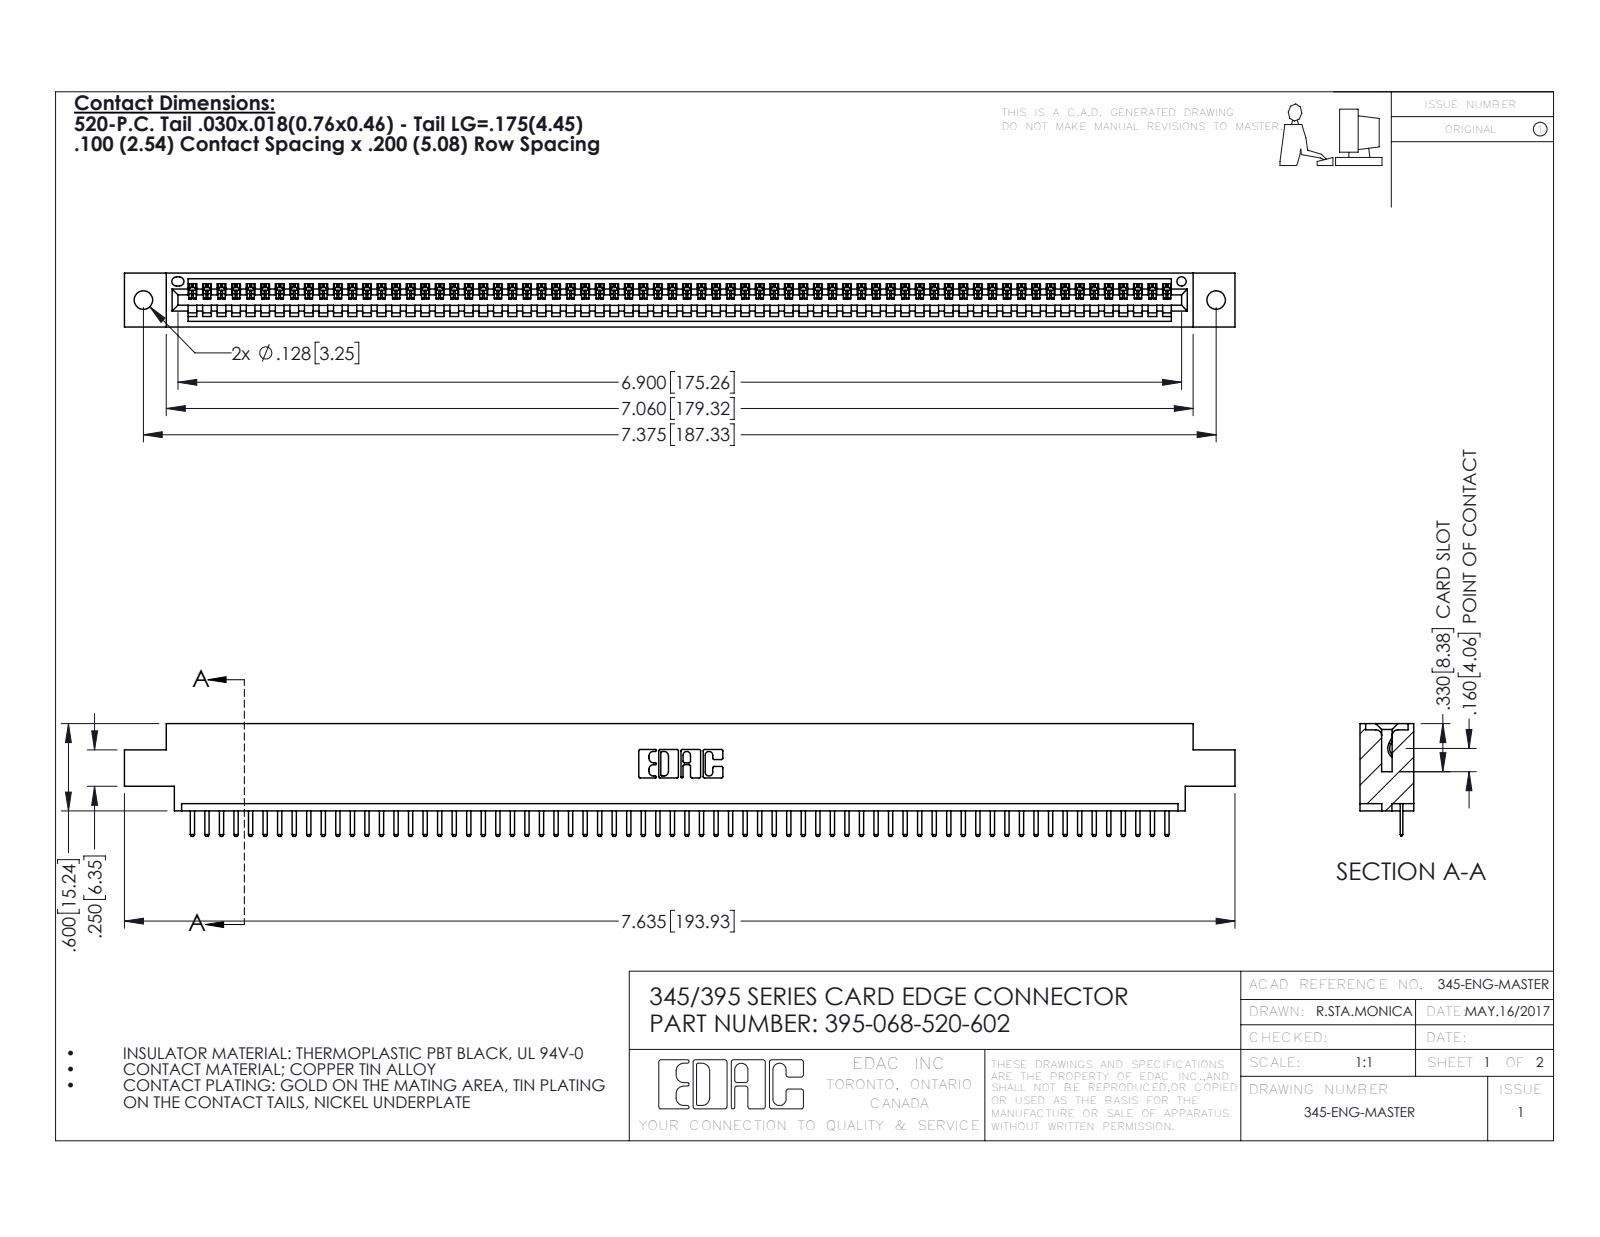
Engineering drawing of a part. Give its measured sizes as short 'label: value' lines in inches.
name: 345-292-001_345-293-120; 395-068-520-602; 345 Part_0.170 Offset - 0.128 Dia
written by: SolidWorks 2016 (CONFIG_CONTROL_DESIGN)
unit: in
bodies: 69 solids, 4346 faces (2940 planar, 1406 cylindrical, 0 other)
size: 7.635 × 0.775 × 0.37
volume: 1.116 in³; area: 37 in²
holes: 2× ⌀0.128, 1× ⌀0.064
rounds: 138× R0.01, 136× R0.006, 22× R0.01, 6× R0.007, 6× R0.031, 3× R0.026, 2× R0.031, 2× R0.04
face distances: 0.298, 0.072, 0.37, 0.2, 0.098, 0.272, 0.025, 0.225, 0.072, 0.175
hole spacings: 0.27, 7.139, 7.375
